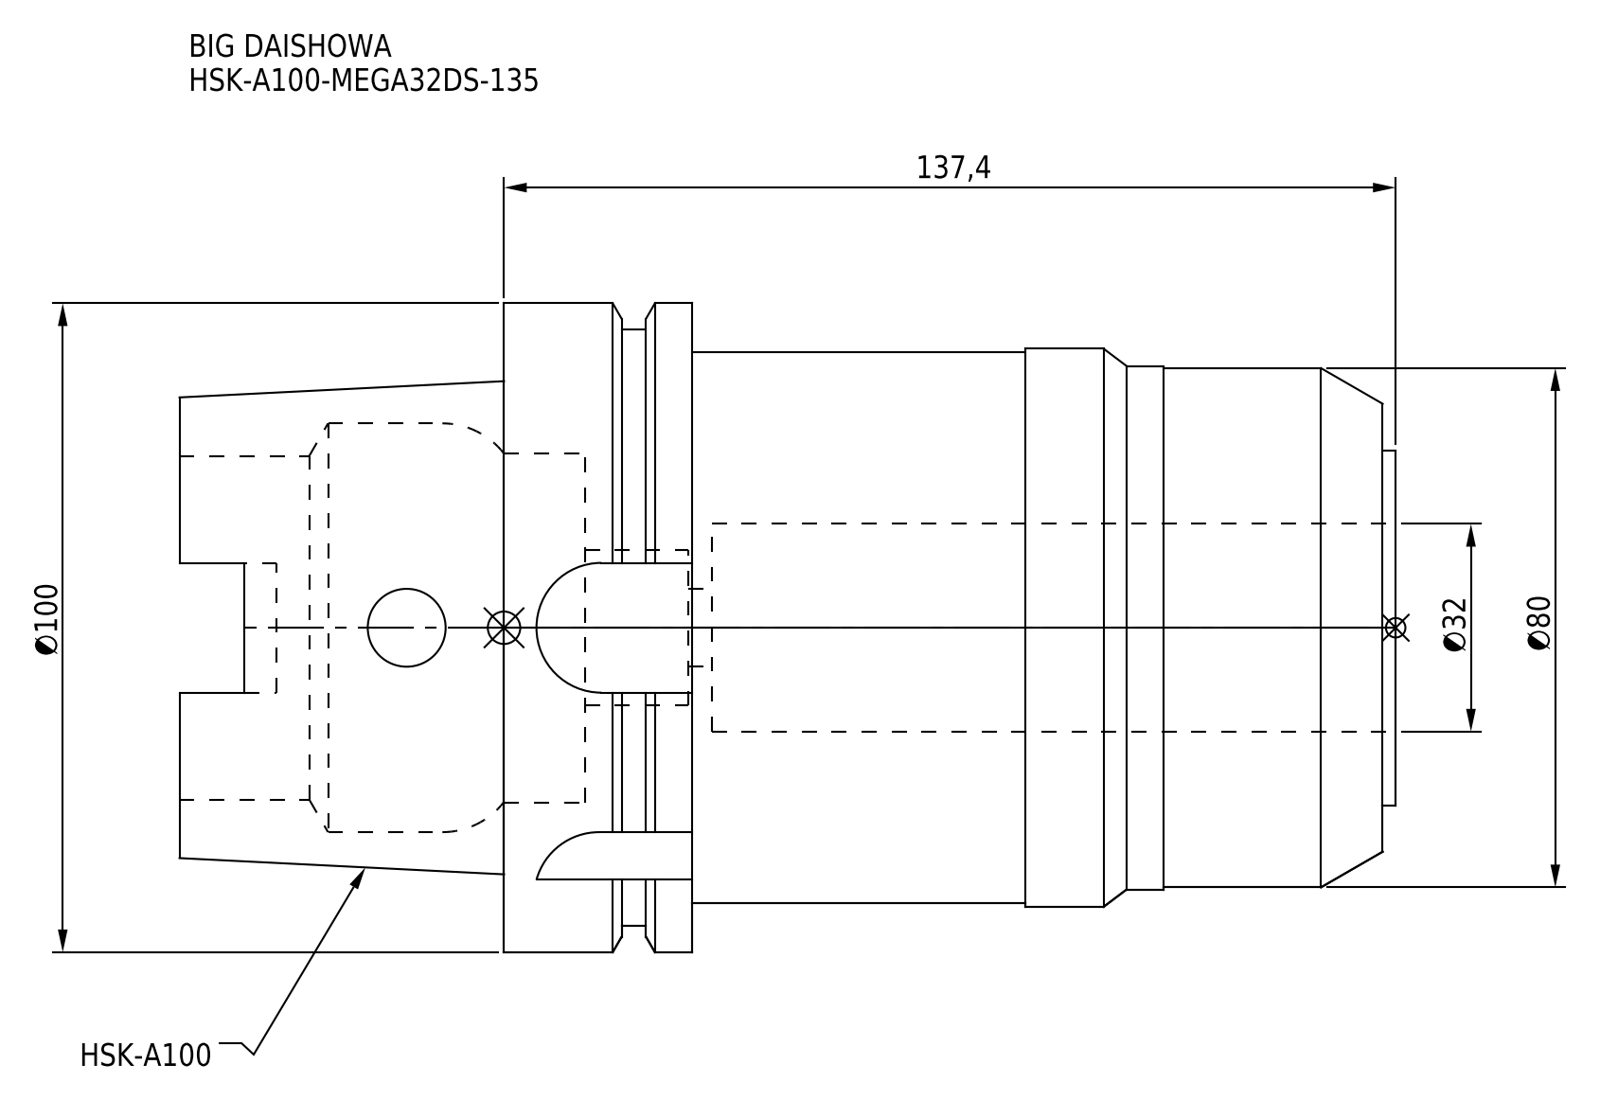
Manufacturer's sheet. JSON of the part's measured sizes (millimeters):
{"part_name": "HSK-A100-MEGA32DS-135", "step_written_by": "CREO PARAMETRIC BY PTC INC, 2016380 (AUTOMOTIVE_DESIGN)", "units": "millimeters", "bodies": {"solids": 1, "faces": 98, "planar": 36, "cylindrical": 44, "other": 18}, "overall_size": [187.4, 100, 100], "volume_mm3": 746314, "surface_area_mm2": 87369, "round_holes": [[12, 2], [24, 1], [32, 1], [53, 1], [53.8, 1], [63, 1]], "round_bosses_or_shafts": [[100, 1], [92, 1], [86, 1], [85, 1], [80.7, 1], [80, 1], [54.7, 1]], "partial_cylinders_radius": [[4.88, 4], [10, 4]], "face_to_face_distances": [29, 16.55, 12.45, 108.4, 124.95, 137.4, 2, 106.4, 122.95, 135.4]}
